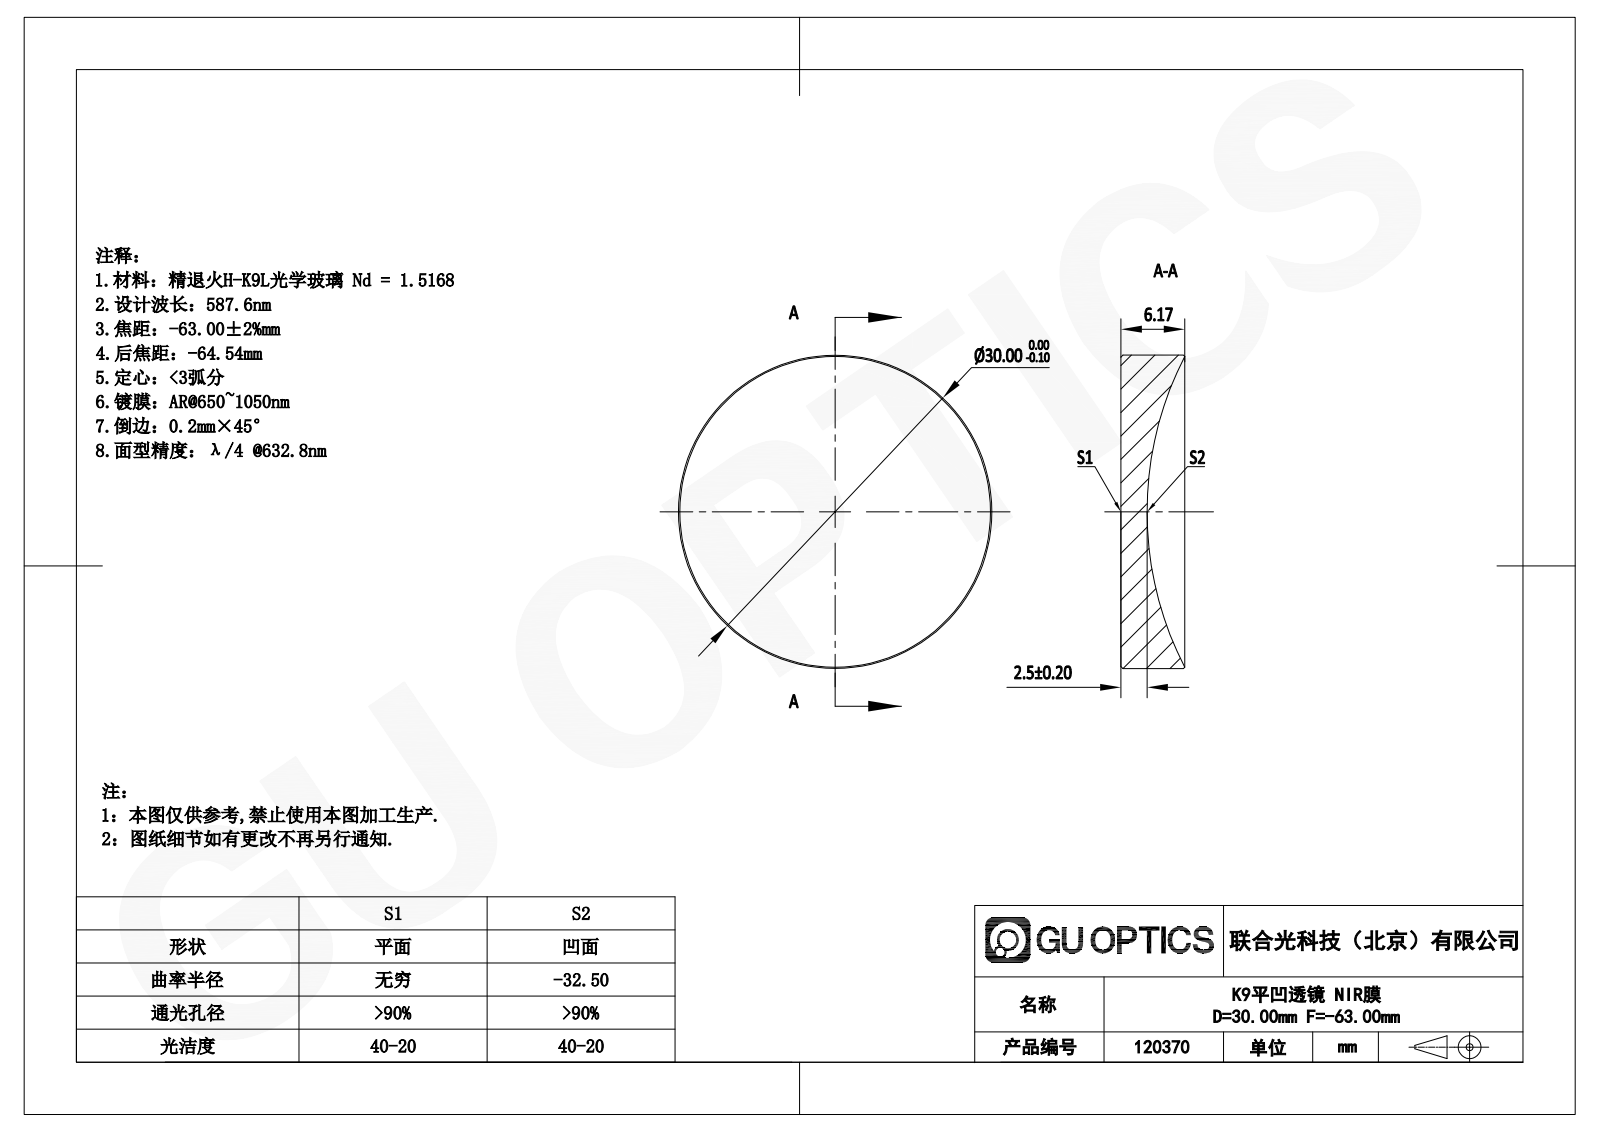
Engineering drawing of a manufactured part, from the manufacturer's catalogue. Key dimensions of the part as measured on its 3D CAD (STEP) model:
Part name (STEP PRODUCT): GL13-030-063
STEP written by: SolidWorks 2022 (AUTOMOTIVE_DESIGN)
Units: millimetres
Bodies: 1 solid, 9 faces (1 planar, 2 cylindrical, 6 other)
Overall size (bounding box): 30 × 30 × 6.1
Volume: 3 035 mm³ · Surface area: 2 011 mm²
Round bosses / shafts (diameter × count): ⌀30 ×1
